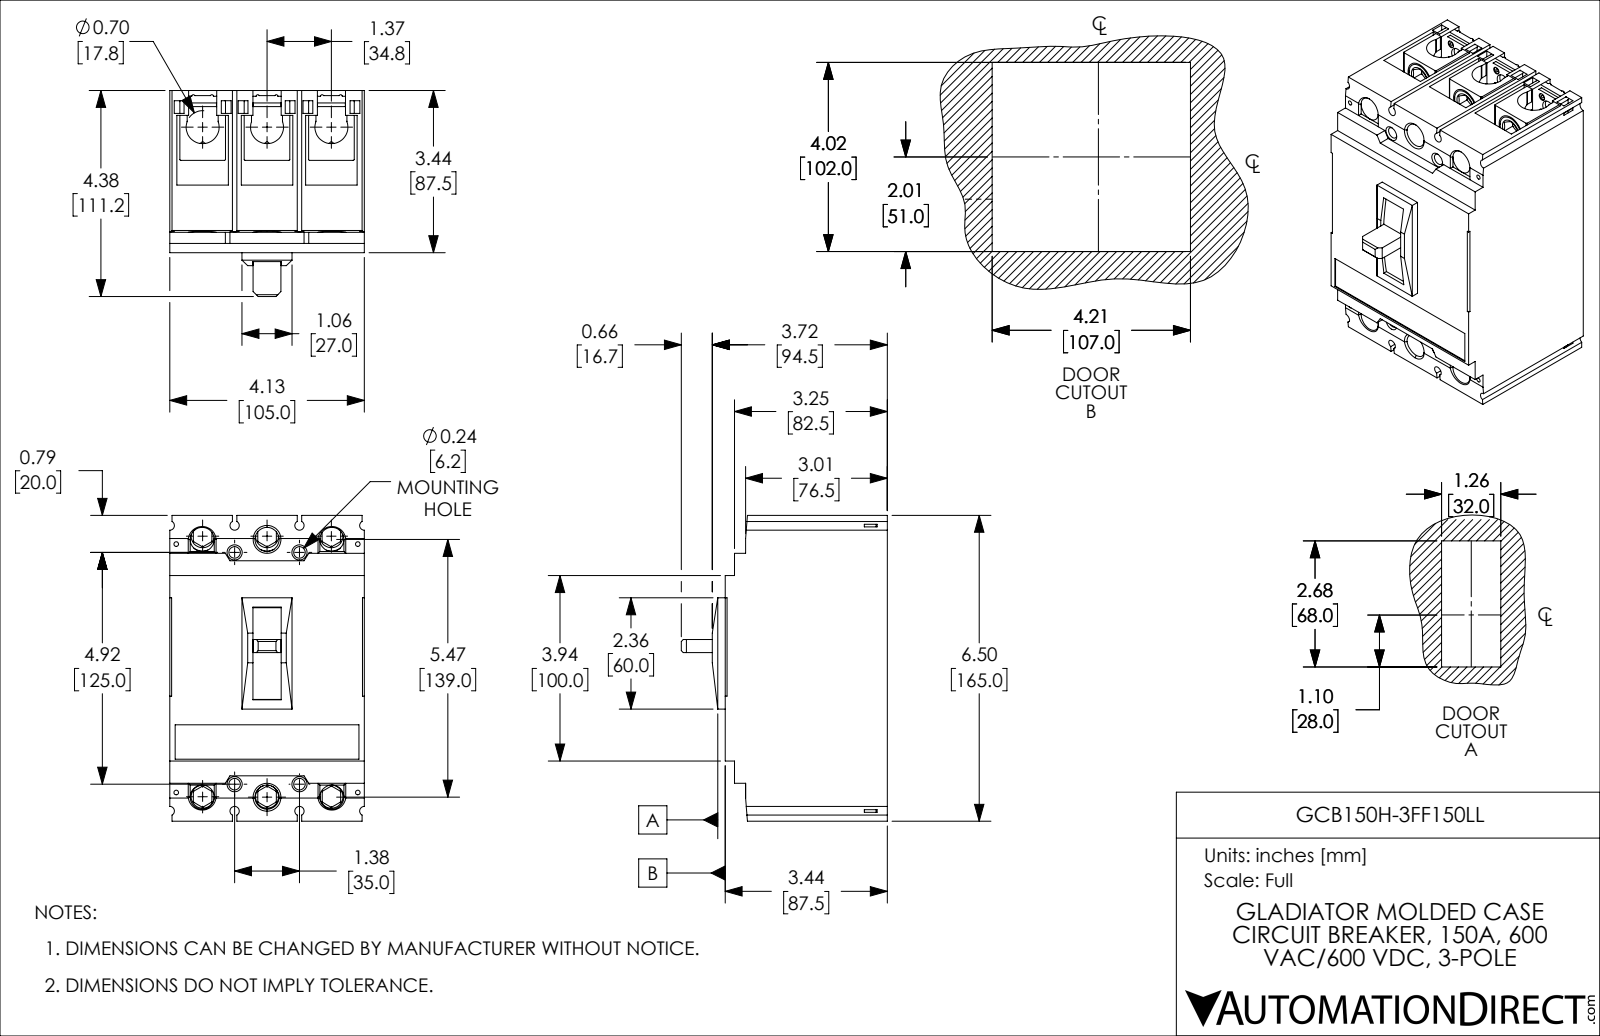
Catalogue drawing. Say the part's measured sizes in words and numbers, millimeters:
The part is named "GCB150H-3FF150LL". Its 3-D file was written by "SolidWorks 2021 (CONFIG_CONTROL_DESIGN)". It is 19 solids with 1004 faces: 544 planar, 381 cylindrical and 79 other. Overall it measures 165 by 111.2 by 105 millimeters. Its volume is 1 312 000 cubic millimeters and its surface area 160 100 square millimeters. Round holes: 24 of diameter 1.7, 24 of diameter 4, 10 of diameter 2.5, 6 of diameter 9, 6 of diameter 13, 6 of diameter 17.5, 4 of diameter 5, 4 of diameter 6.2. Round bosses or shafts: 6 of diameter 18. Partial cylindrical surfaces (rounded edges, fillets, slot ends): 36 of radius 1, 24 of radius 0.2, 6 of radius 0.4, 6 of radius 0.5, 6 of radius 0.8, 4 of radius 2.5, 3 of radius 8.9, 1 of radius 143.2. The main face-to-face distances are 34.7, 105, 1.6, 26.2, 21.5, 22, 87.5, 143, 69.5, 6.7. The hole center spacings are 35, 7.2, 34.7, 14.5, 18.8, 19.1, 133.1, 147.5.
